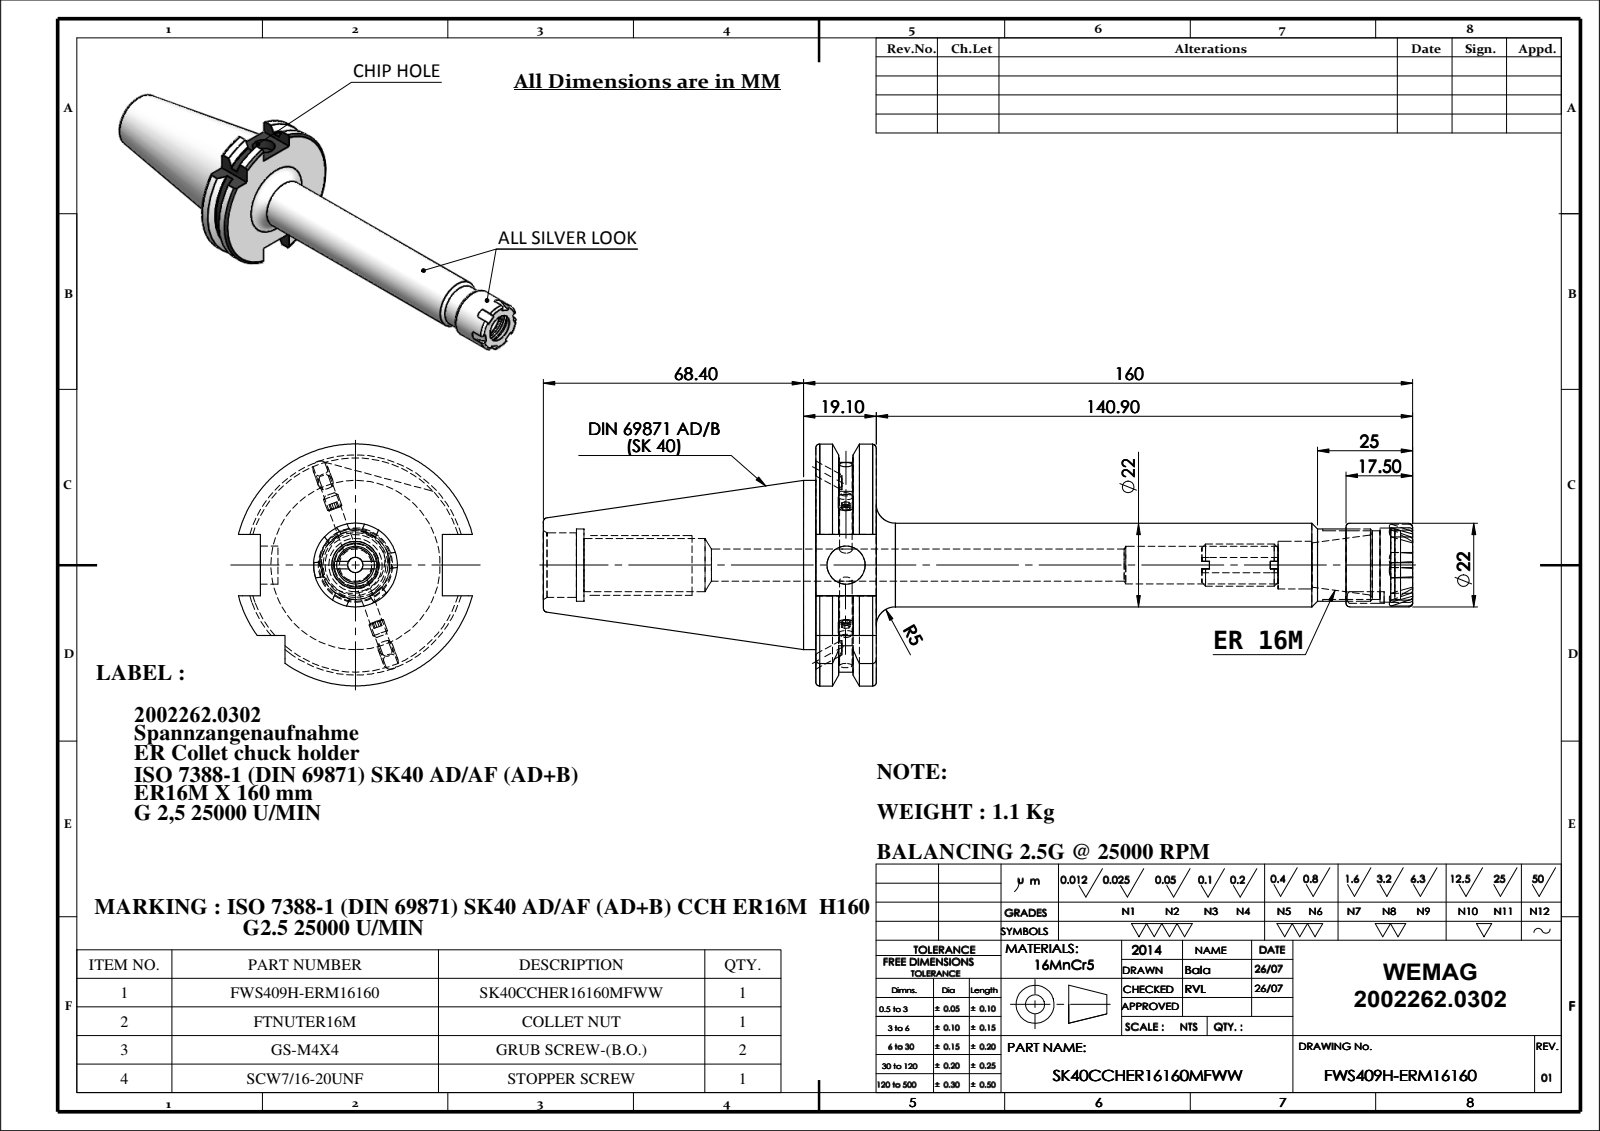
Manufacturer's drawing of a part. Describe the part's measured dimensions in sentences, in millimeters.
The part is named "FTNUTER16M; SK40CCHER16160MFWW; M4X4; FTSCW71620 (+2 more)". Its 3-D file was written by "SolidWorks 2018 (CONFIG_CONTROL_DESIGN)". It is 5 solids with 210 faces: 92 planar, 54 cylindrical and 64 other. Overall it measures 228.4 by 63.55 by 61.48 millimeters. Its volume is 144 628 cubic millimeters and its surface area 37 349 square millimeters. Round holes: 2 of diameter 17, 1 of diameter 3.3, 1 of diameter 4, 1 of diameter 8.5, 1 of diameter 9.92, 1 of diameter 10, 1 of diameter 12.5, 1 of diameter 14, 1 of diameter 18, 1 of diameter 19, 1 of diameter 19.5. Round bosses or shafts: 1 of diameter 44.45, 1 of diameter 22, 1 of diameter 11.1, 1 of diameter 4. Partial cylindrical surfaces (rounded edges, fillets, slot ends): 1 of radius 28.12, 1 of radius 31.77. The main face-to-face distances are 15.9, 16.1, 47.8, 140.9, 156.8, 228.4, 87.5, 71.6, 217.7, 76.8. The hole center spacings are 1.3.
